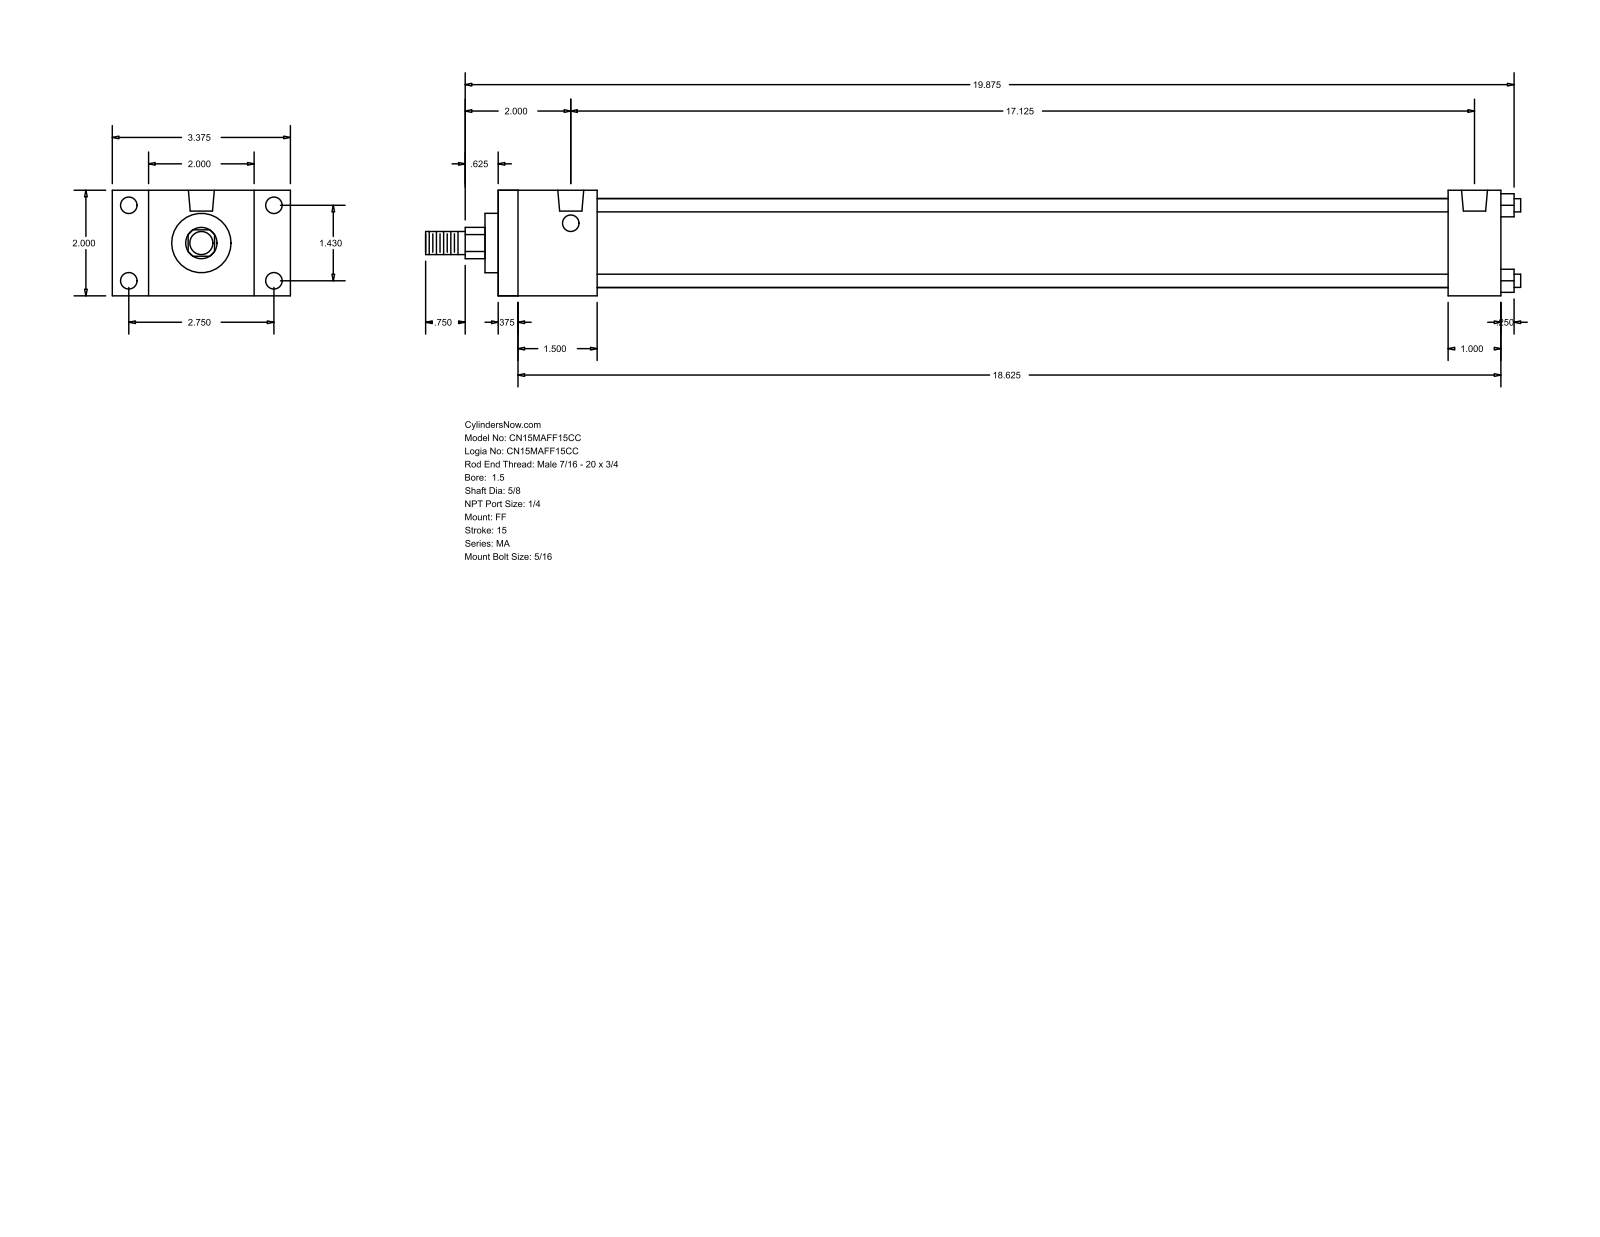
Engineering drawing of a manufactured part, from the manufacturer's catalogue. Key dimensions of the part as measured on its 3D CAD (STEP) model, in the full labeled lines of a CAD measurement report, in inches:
Part name (STEP PRODUCT): MA_FF__0150_0.625
STEP written by: GSSL Pune (CONFIG_CONTROL_DESIGN)
Units: inches
Bodies: 0 solids, 92 faces (64 planar, 28 cylindrical, 0 other)
Overall size (bounding box): 20.75 × 3.375 × 2
Round holes (diameter × count): ⌀0.313 ×8, ⌀0.492 ×2
Round bosses / shafts (diameter × count): ⌀0.25 ×4, ⌀1.69 ×1, ⌀1.125 ×1, ⌀0.625 ×1, ⌀0.437 ×1
Partial cylindrical surfaces — rounded edges, fillets, slot ends (radius × count): R0.297 ×1
Main face-to-face distances: 2, 19, 0.375, 18.625, 1.875, 18, 1.5, 17.625, 16.125, 17.125
Hole centre spacings: 1.43, 2.75, 3.099, 17.125
